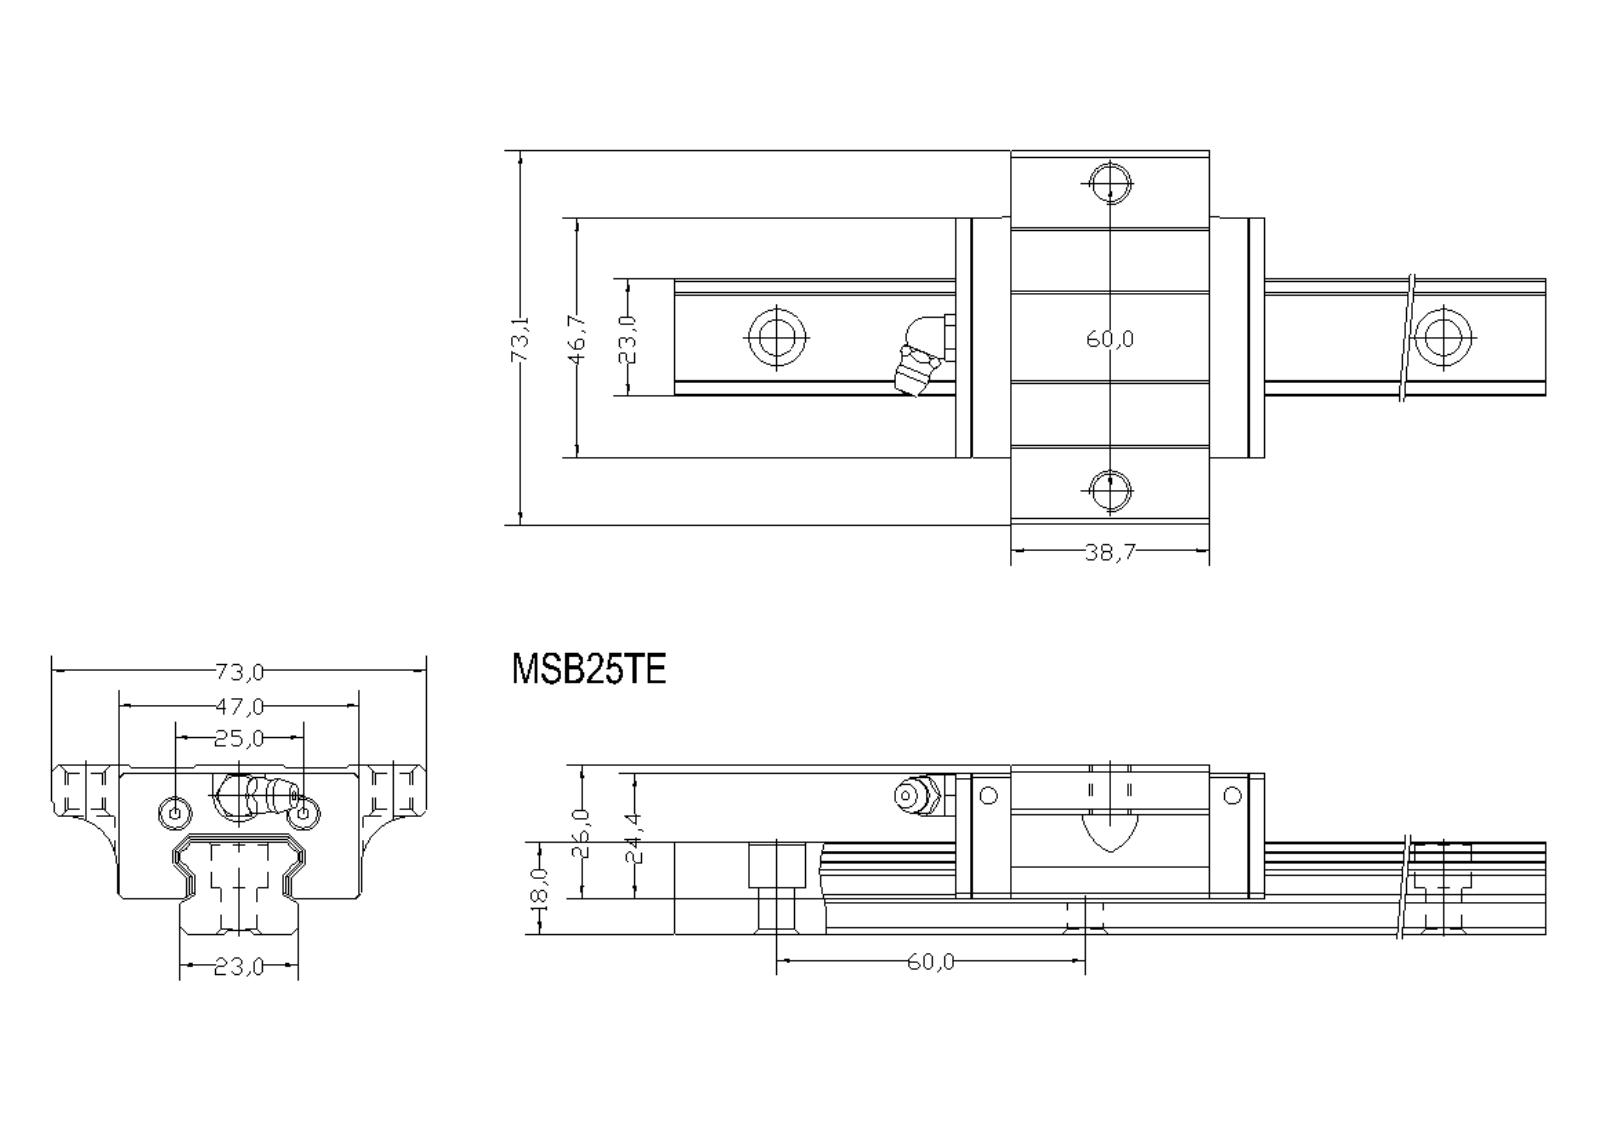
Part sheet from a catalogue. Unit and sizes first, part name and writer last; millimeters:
Units: millimetres
Overall size (bounding box): 220 × 73 × 33
Round holes (diameter × count): ⌀7 ×4, ⌀11 ×4, ⌀6.5 ×3, ⌀8 ×2
Round bosses / shafts (diameter × count): ⌀8 ×1
Partial cylindrical surfaces — rounded edges, fillets, slot ends (radius × count): R2.2 ×4, R5.75 ×2, R10 ×2, R5.05 ×1
Main face-to-face distances: 18, 2.8, 20.2, 17.4, 33, 15, 7, 11, 26, 32.5
Hole centre spacings: 42.43, 60, 94.87, 12.98, 120, 25, 180
Volume: 143 387 mm³ · Surface area: 37 585 mm²
Bodies: 3 solids, 206 faces (137 planar, 52 cylindrical, 17 other)
STEP written by: Kubotek KeyCreator V6.5.2 (0407) (CONFIG_CONTROL_DESIGN)
